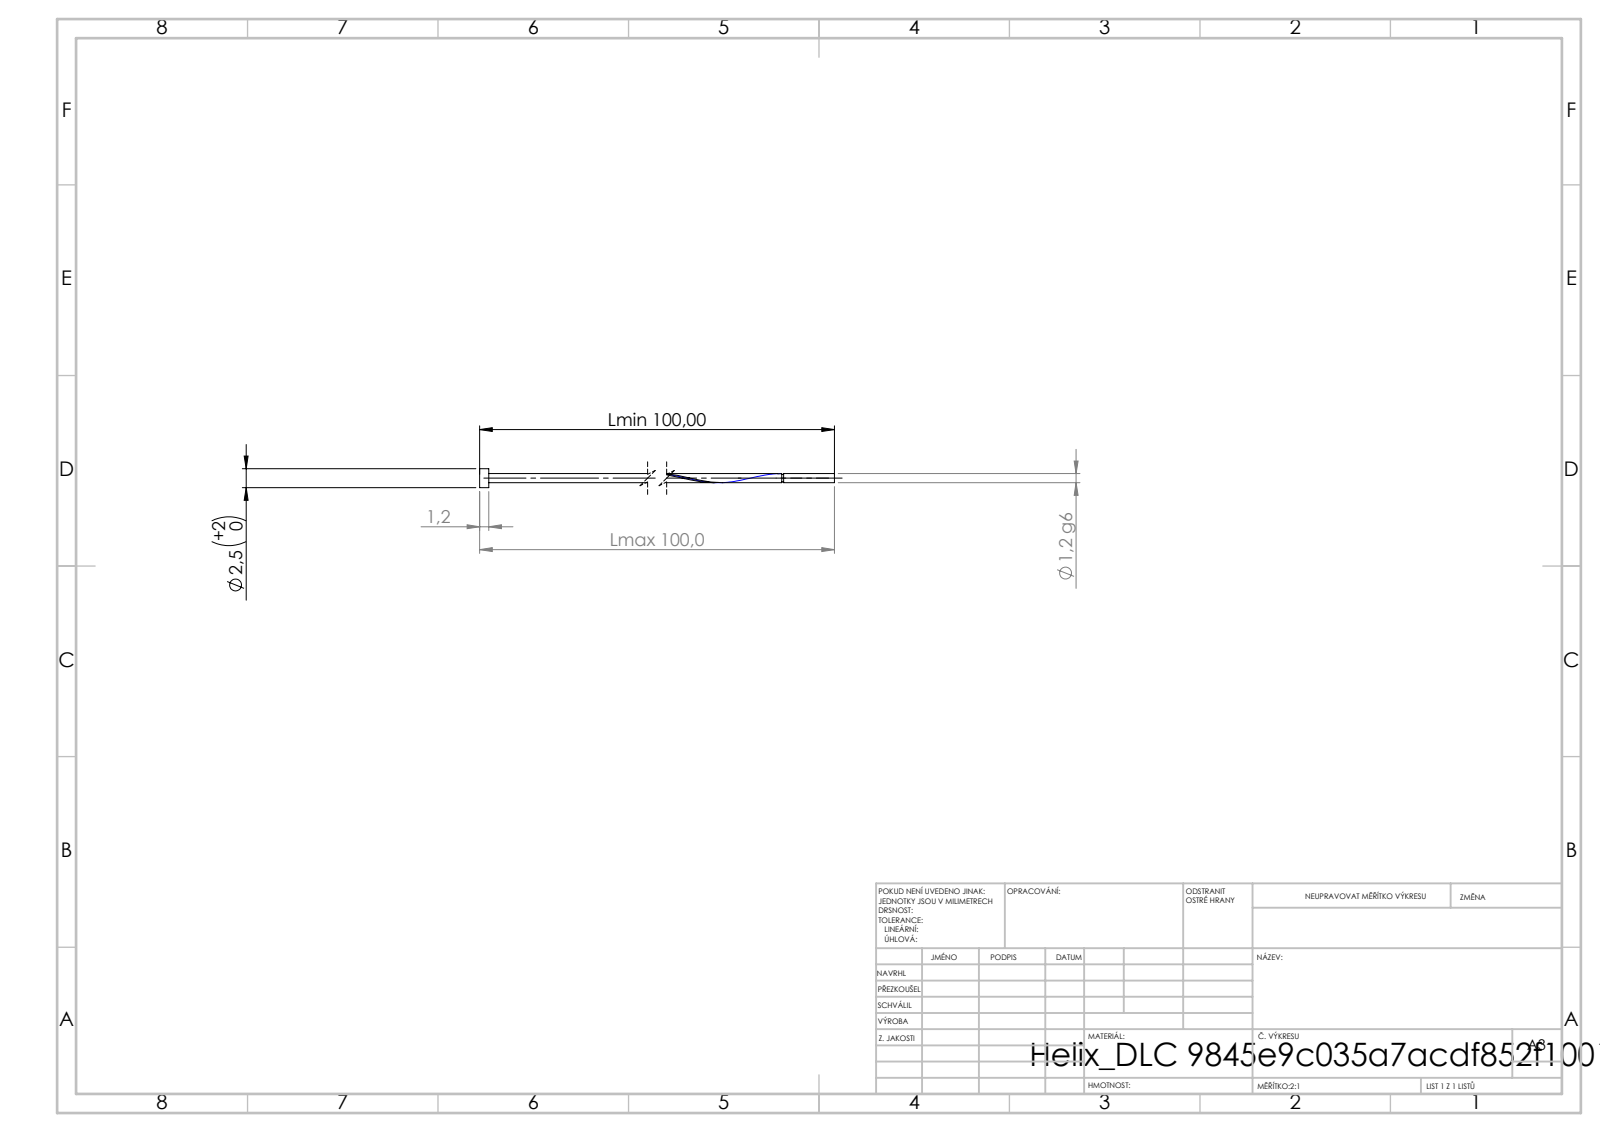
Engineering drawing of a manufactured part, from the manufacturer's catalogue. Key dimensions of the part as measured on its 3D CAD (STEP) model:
STEP written by: SolidWorks 2019 (CONFIG_CONTROL_DESIGN)
Units: millimetres
Bodies: 1 solid, 16 faces (6 planar, 9 cylindrical, 1 other)
Overall size (bounding box): 100 × 2.5 × 2.5
Volume: 142 mm³ · Surface area: 524 mm²
Round bosses / shafts (diameter × count): ⌀2.5 ×1, ⌀1.2 ×1, ⌀0.96 ×1
Main face-to-face distances: 1.2, 100, 98.8, 93.33, 92.13, 6.67, 93.09, 91.89, 6.91, 43.09
